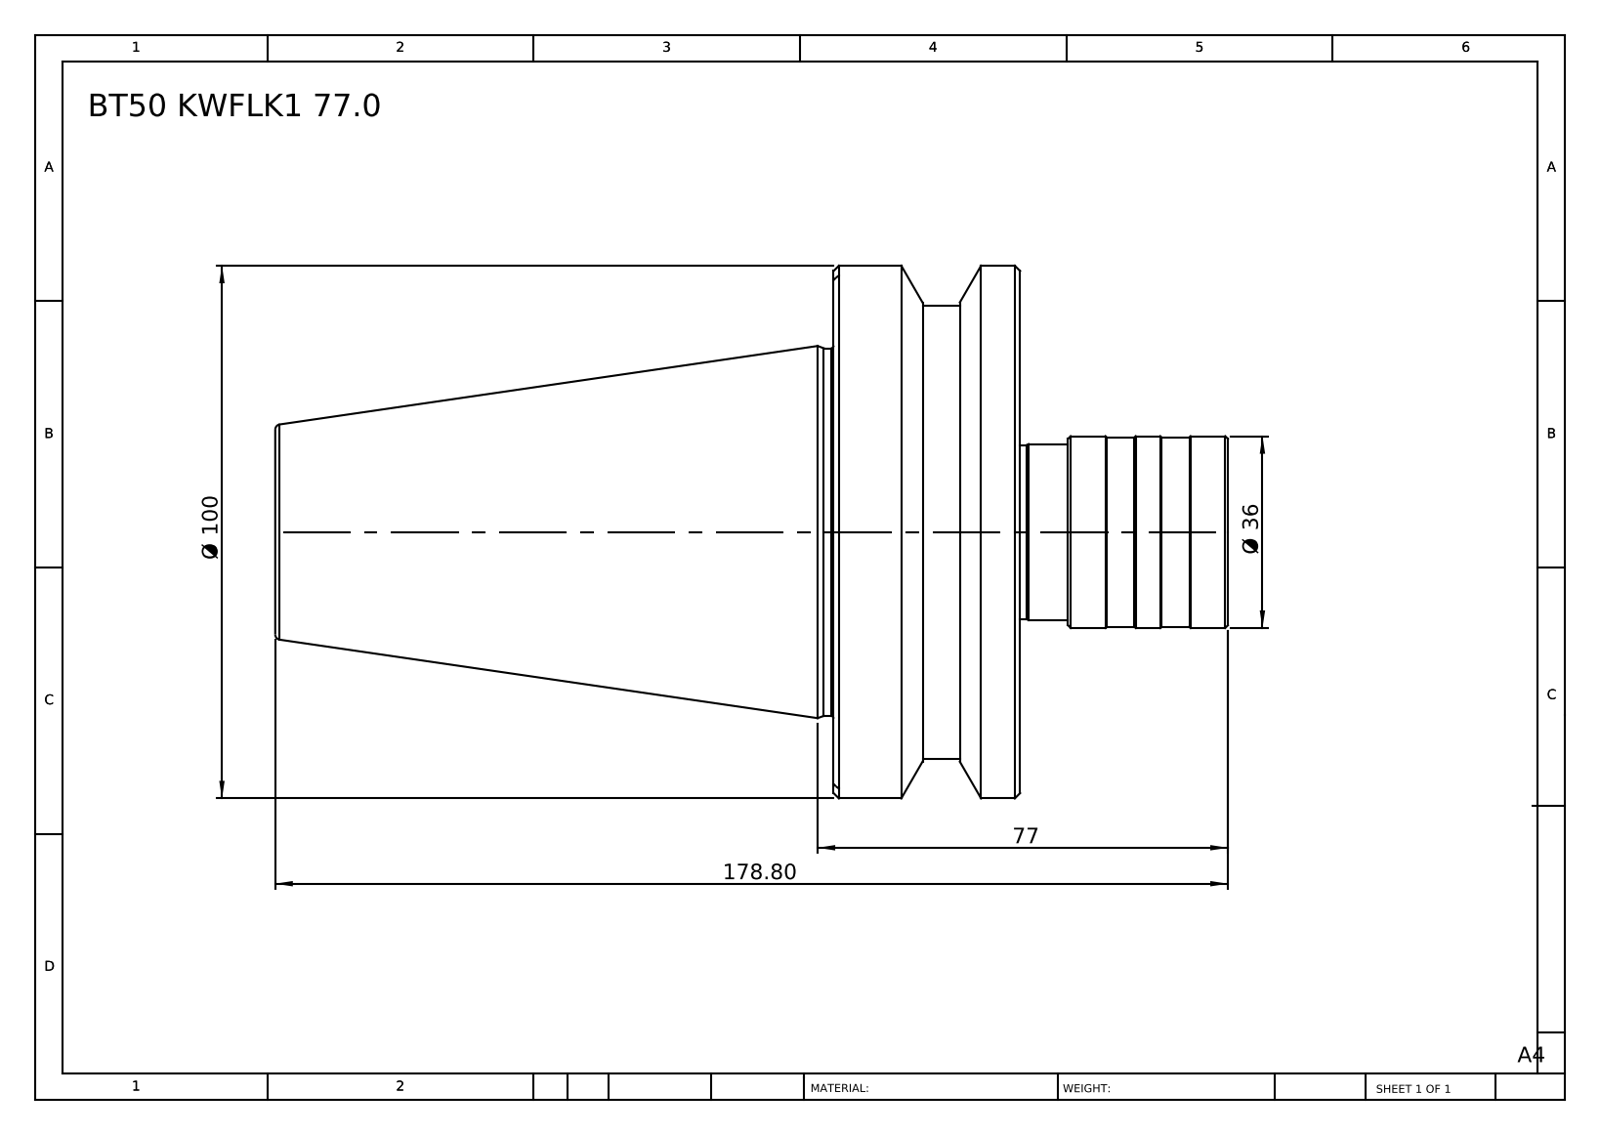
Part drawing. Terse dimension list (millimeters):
name: BT50 KWFLK1 77.0
written by: SolidWorks 2014 (CONFIG_CONTROL_DESIGN)
unit: mm
bodies: 1 solid, 62 faces (7 planar, 22 cylindrical, 33 other)
size: 178.8 × 100 × 100
volume: 547 961 mm³; area: 49 004 mm²
bosses: 1× ⌀100, 1× ⌀85, 1× ⌀69, 1× ⌀36, 1× ⌀35.5, 1× ⌀33, 1× ⌀32.6
face distances: 35, 139.8, 104.8, 39, 74, 178.8, 50.3, 11.3, 23.7, 128.5
